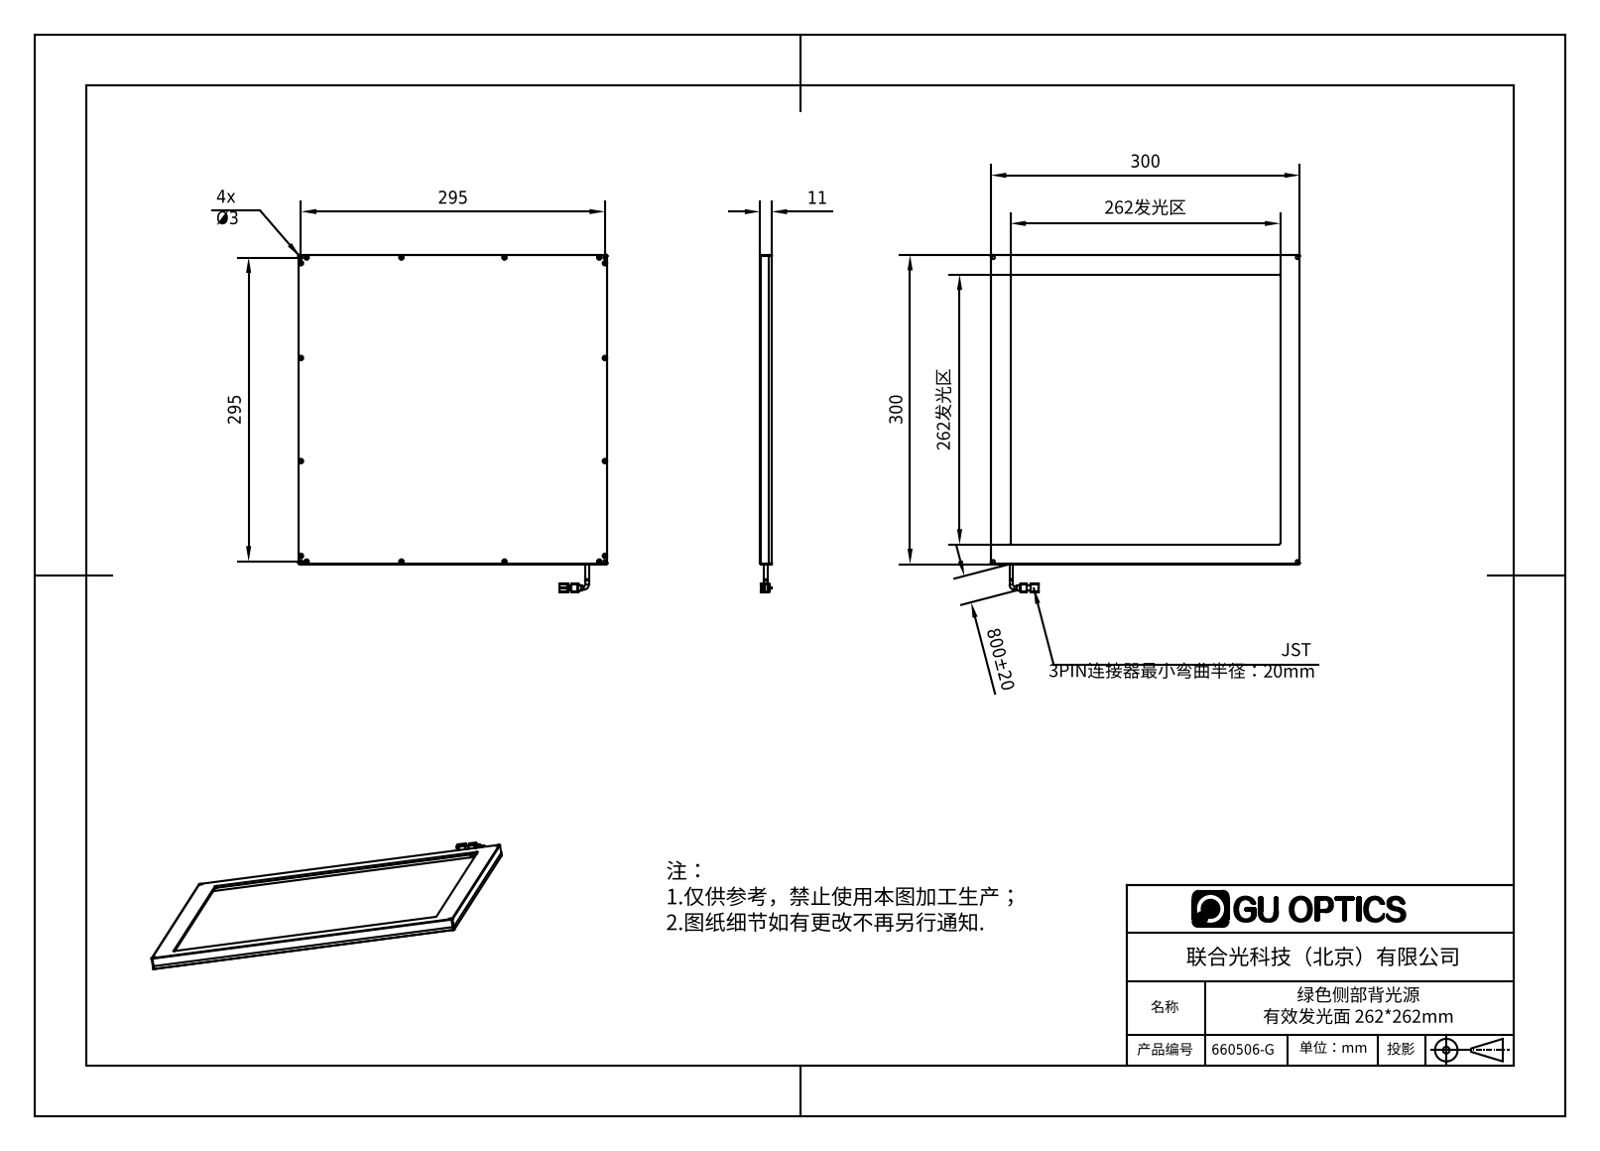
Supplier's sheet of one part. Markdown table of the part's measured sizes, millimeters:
| quantity | value |
| --- | --- |
| part name | 660506-G |
| STEP written by | SolidWorks 2016 (AUTOMOTIVE_DESIGN) |
| units | millimeters |
| bodies | 4 solids, 447 faces (176 planar, 146 cylindrical, 125 other) |
| overall size | 327 × 300 × 11 |
| volume | 337 644 mm³ |
| surface area | 246 818 mm² |
| round holes (diameter × count) | 1.6 × 16, 2 × 16, 2.4 × 16, 3 × 4 |
| round bosses / shafts (diameter × count) | 3.5 × 2 |
| partial cylindrical surfaces (radius × count) | 0.5 × 10, 1 × 8, 1.5 × 4, 2 × 2 |
| main face-to-face distances | 3, 8, 11, 1.8, 6.2, 9.2, 4, 296, 300, 292 |
| hole center spacings | 295, 5.5, 92, 97.5, 97.66, 192, 197.5, 197.58 |
